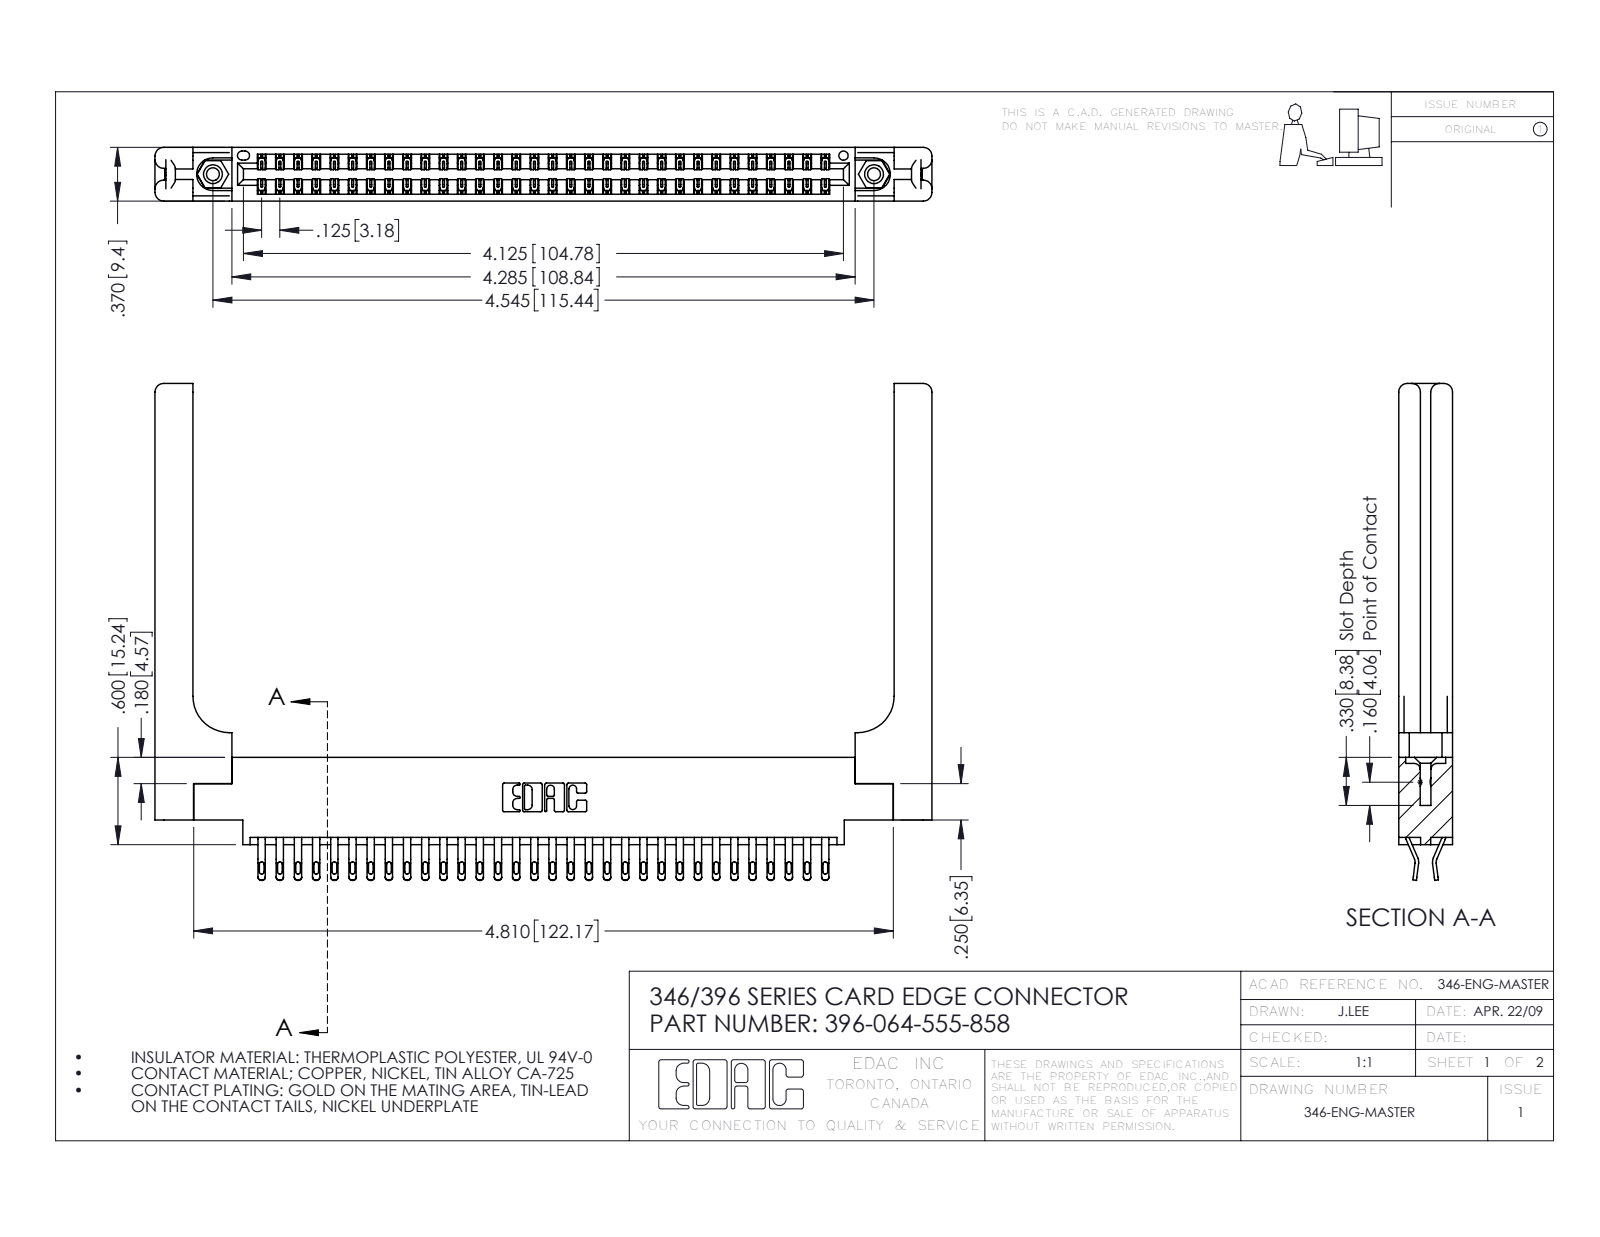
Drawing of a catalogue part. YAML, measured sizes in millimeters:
part_name: "345-250-001_345-250-001-102; 346 Part_0.170 Offset - 0.156 Dia-TH; 396-064-555-858; 345-292-001_555 Tail (+1 more)"
step_written_by: "SolidWorks 2016 (CONFIG_CONTROL_DESIGN)"
units: millimeters
bodies: {solids: 69, faces: 4094, planar: 2340, cylindrical: 1694, other: 60}
overall_size: [135.7, 86.7, 9.4]
volume: 20680
surface_area: 23770
round_holes:
  - {diameter: 2.3, count: 2}
  - {diameter: 3.2, count: 2}
  - {diameter: 4, count: 2}
  - {diameter: 1.6, count: 1}
round_bosses_or_shafts:
  - {diameter: 3.9, count: 2}
partial_cylinders:
  - {radius: 0.4, count: 128}
  - {radius: 0.5, count: 128}
  - {radius: 0.2, count: 96}
  - {radius: 0.3, count: 22}
  - {radius: 1.5, count: 16}
  - {radius: 0.2, count: 6}
  - {radius: 0.8, count: 6}
  - {radius: 0.7, count: 3}
face_to_face_distances: [9.4, 1.2, 8.2, 1.8, 3.8, 3.8, 6.4, 0.6, 7.6, 7]
hole_center_spacings: [6.2, 110.2, 115.4]
